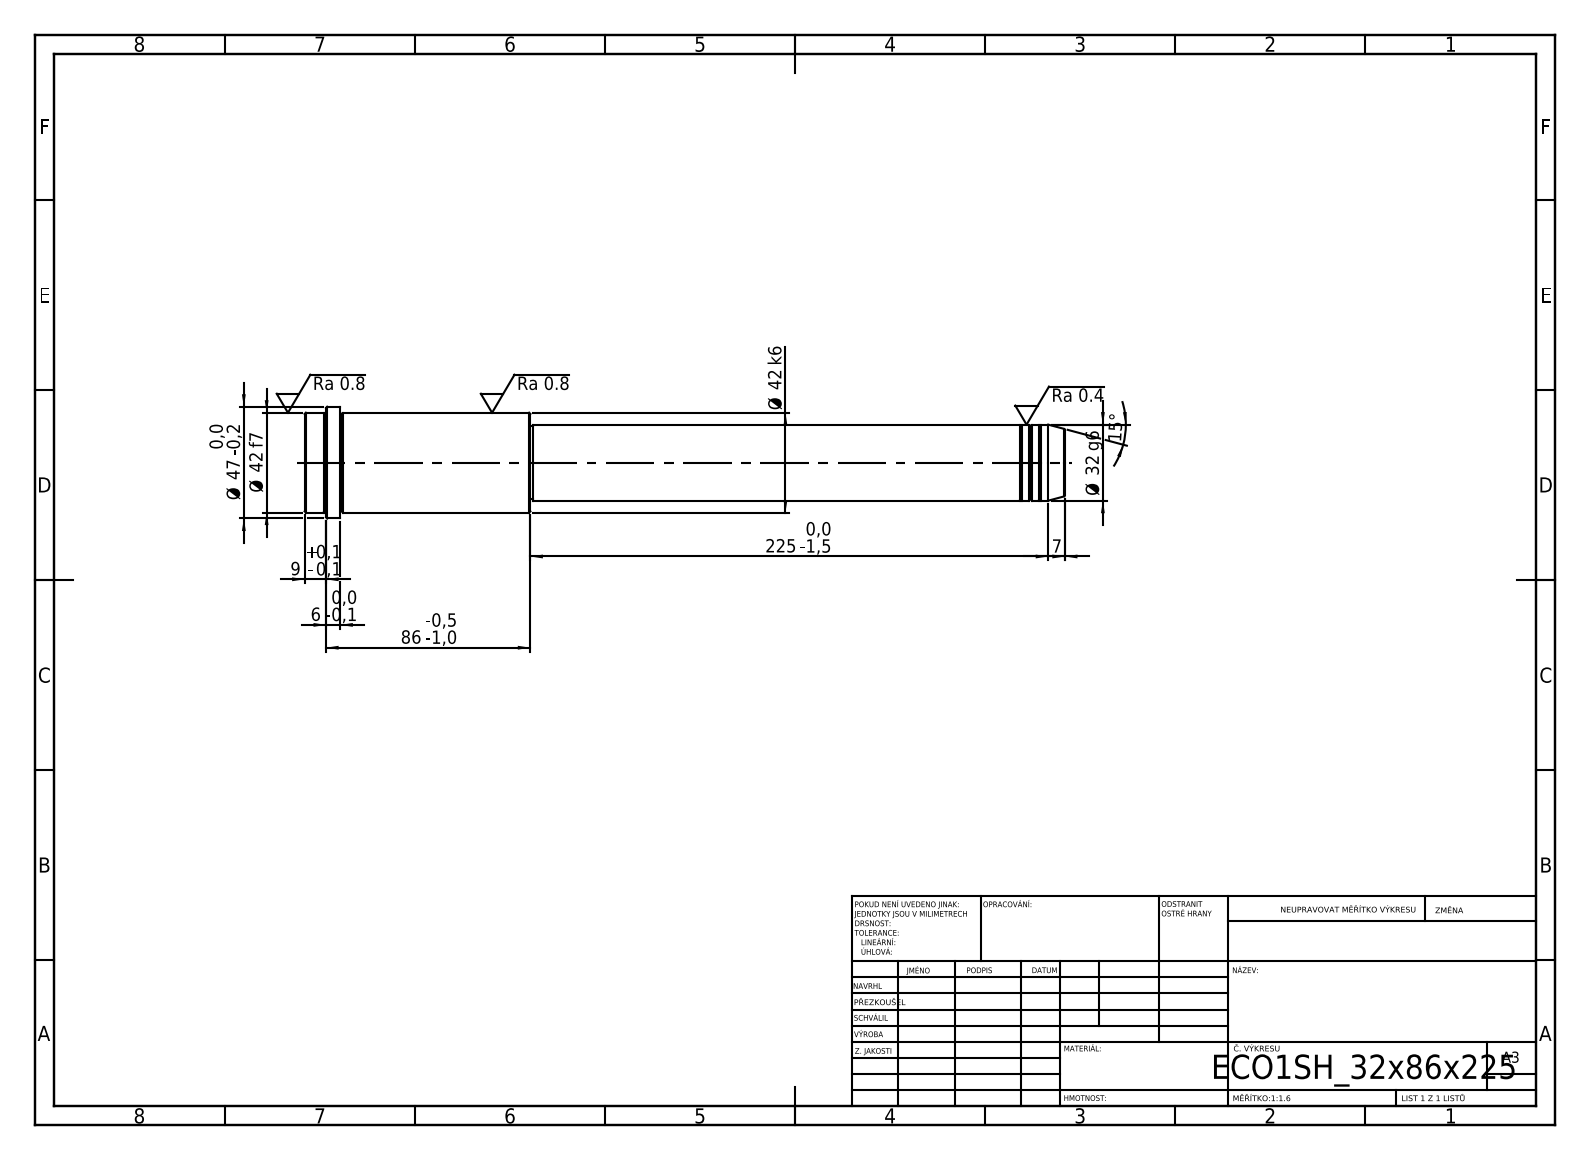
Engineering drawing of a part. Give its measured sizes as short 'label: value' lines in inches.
written by: SolidWorks 2019 (CONFIG_CONTROL_DESIGN)
unit: in
bodies: 1 solid, 52 faces (6 planar, 16 cylindrical, 30 other)
size: 12.598 × 1.85 × 1.85
volume: 19.14 in³; area: 60.13 in²
bosses: 1× ⌀1.85, 1× ⌀1.654, 1× ⌀1.26, 1× ⌀1.22
face distances: 12.598, 8.858, 3.74, 12.008, 3.15, 0.591, 12.244, 3.386, 0.236, 0.354
